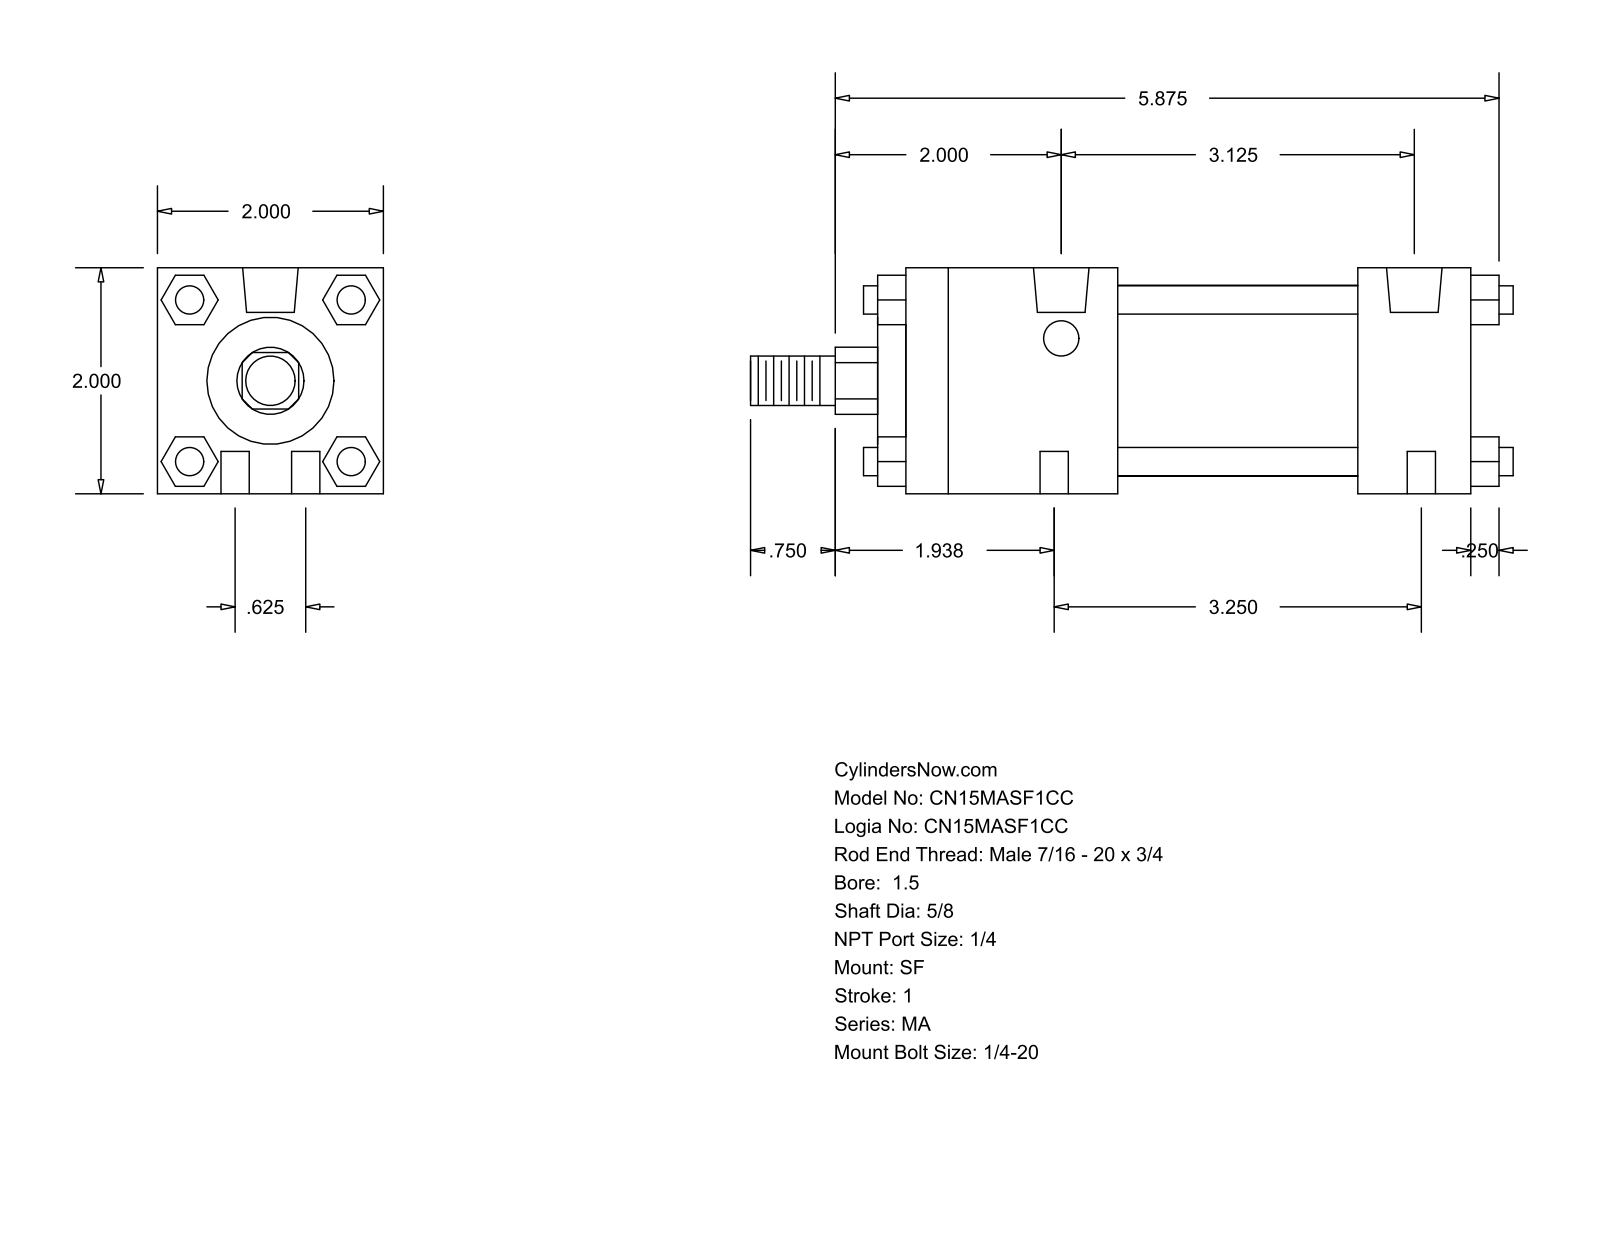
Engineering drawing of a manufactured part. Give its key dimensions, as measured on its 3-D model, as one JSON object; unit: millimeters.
{"part_name": "MA_SF__0150_0.625", "step_written_by": "GSSL Pune (CONFIG_CONTROL_DESIGN)", "units": "millimeters", "bodies": {"solids": 0, "faces": 124, "planar": 94, "cylindrical": 30, "other": 0}, "overall_size": [171.45, 50.8, 50.8], "round_holes": [[6.35, 4], [7.94, 2], [12.49, 2]], "round_bosses_or_shafts": [[6.35, 4], [42.93, 1], [28.57, 1], [15.88, 1], [11.11, 1]], "partial_cylinders_radius": [[7.54, 1]], "face_to_face_distances": [50.8, 53.97, 127, 47.62, 101.59, 79.38, 25.41, 6.35, 107.94, 133.35], "hole_center_spacings": [8.1, 15.88, 79.38, 81.35, 81.36, 82.55, 84.06]}
